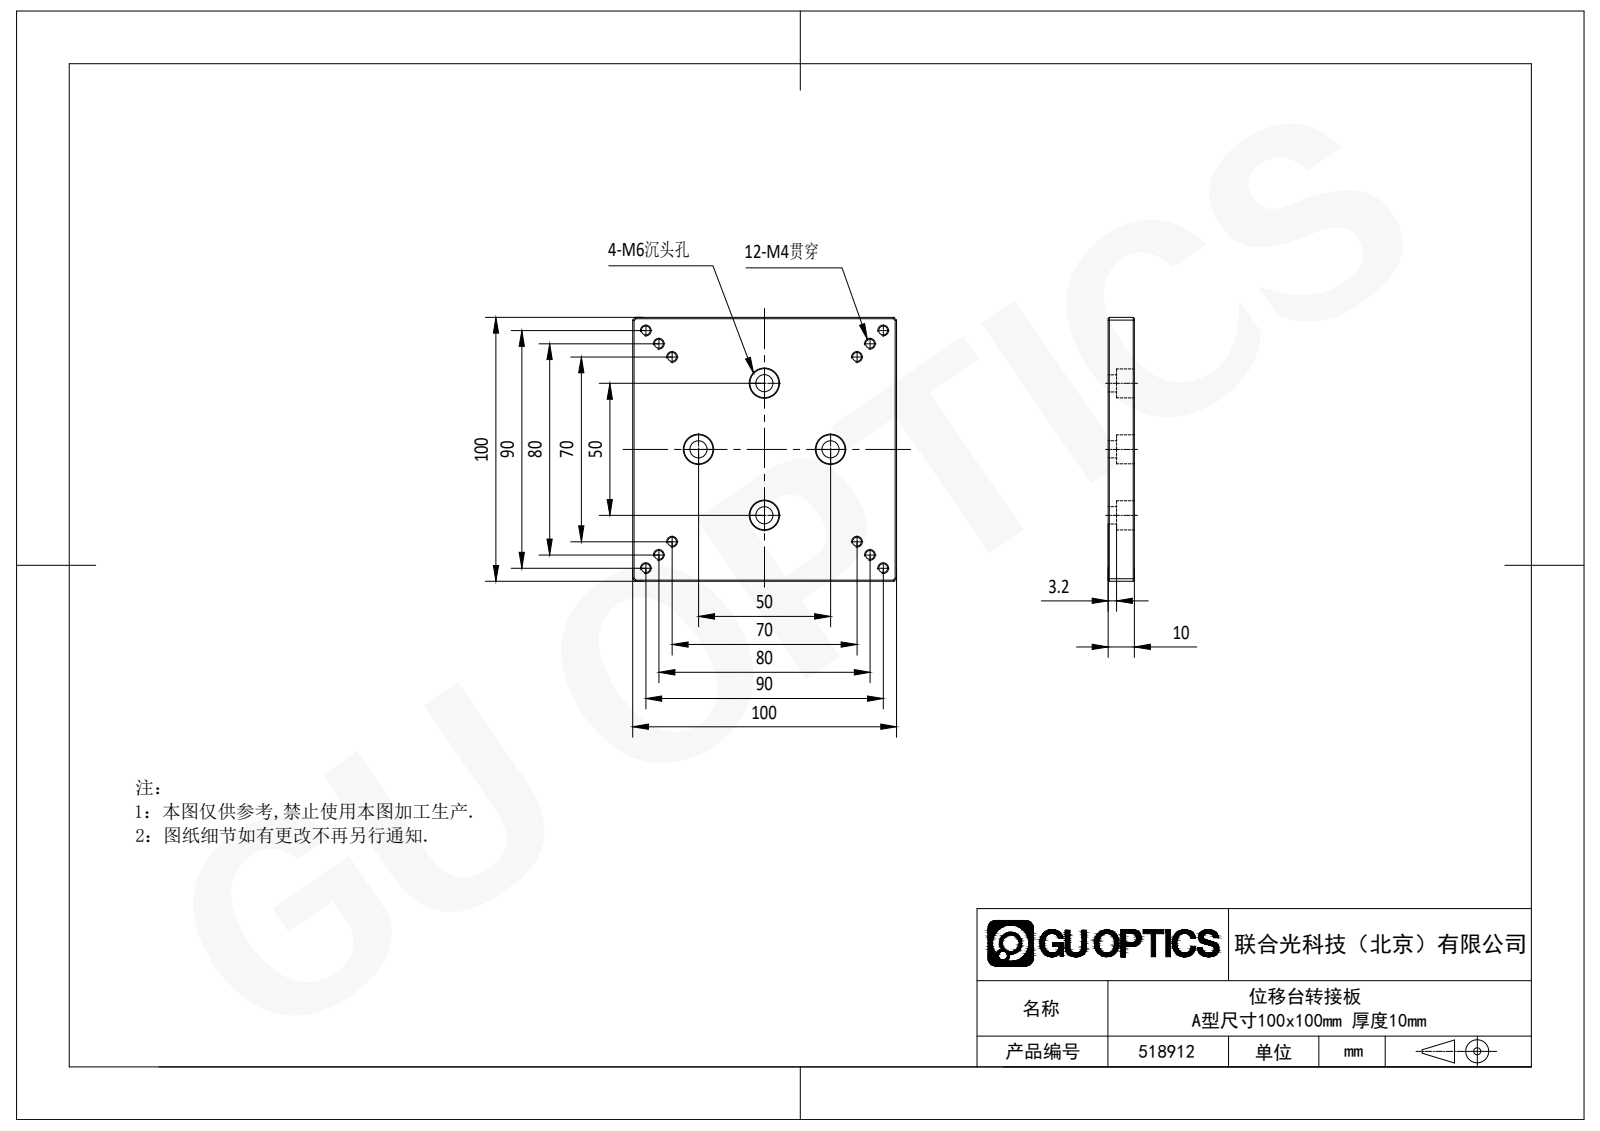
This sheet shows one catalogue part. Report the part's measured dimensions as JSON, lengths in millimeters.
{"step_written_by": "SolidWorks 2020 (CONFIG_CONTROL_DESIGN)", "units": "millimeters", "bodies": {"solids": 1, "faces": 66, "planar": 30, "cylindrical": 20, "other": 16}, "overall_size": [100, 100, 10], "volume_mm3": 95905, "surface_area_mm2": 25652, "round_holes": [[3.3, 12], [6.5, 4], [11, 4]], "face_to_face_distances": [10, 100, 77.07, 3.5, 6.5, 139.98, 105.37], "hole_center_spacings": [7.07, 36.4, 42.72, 49.24, 69.46, 75.17, 76.32, 80.62]}
